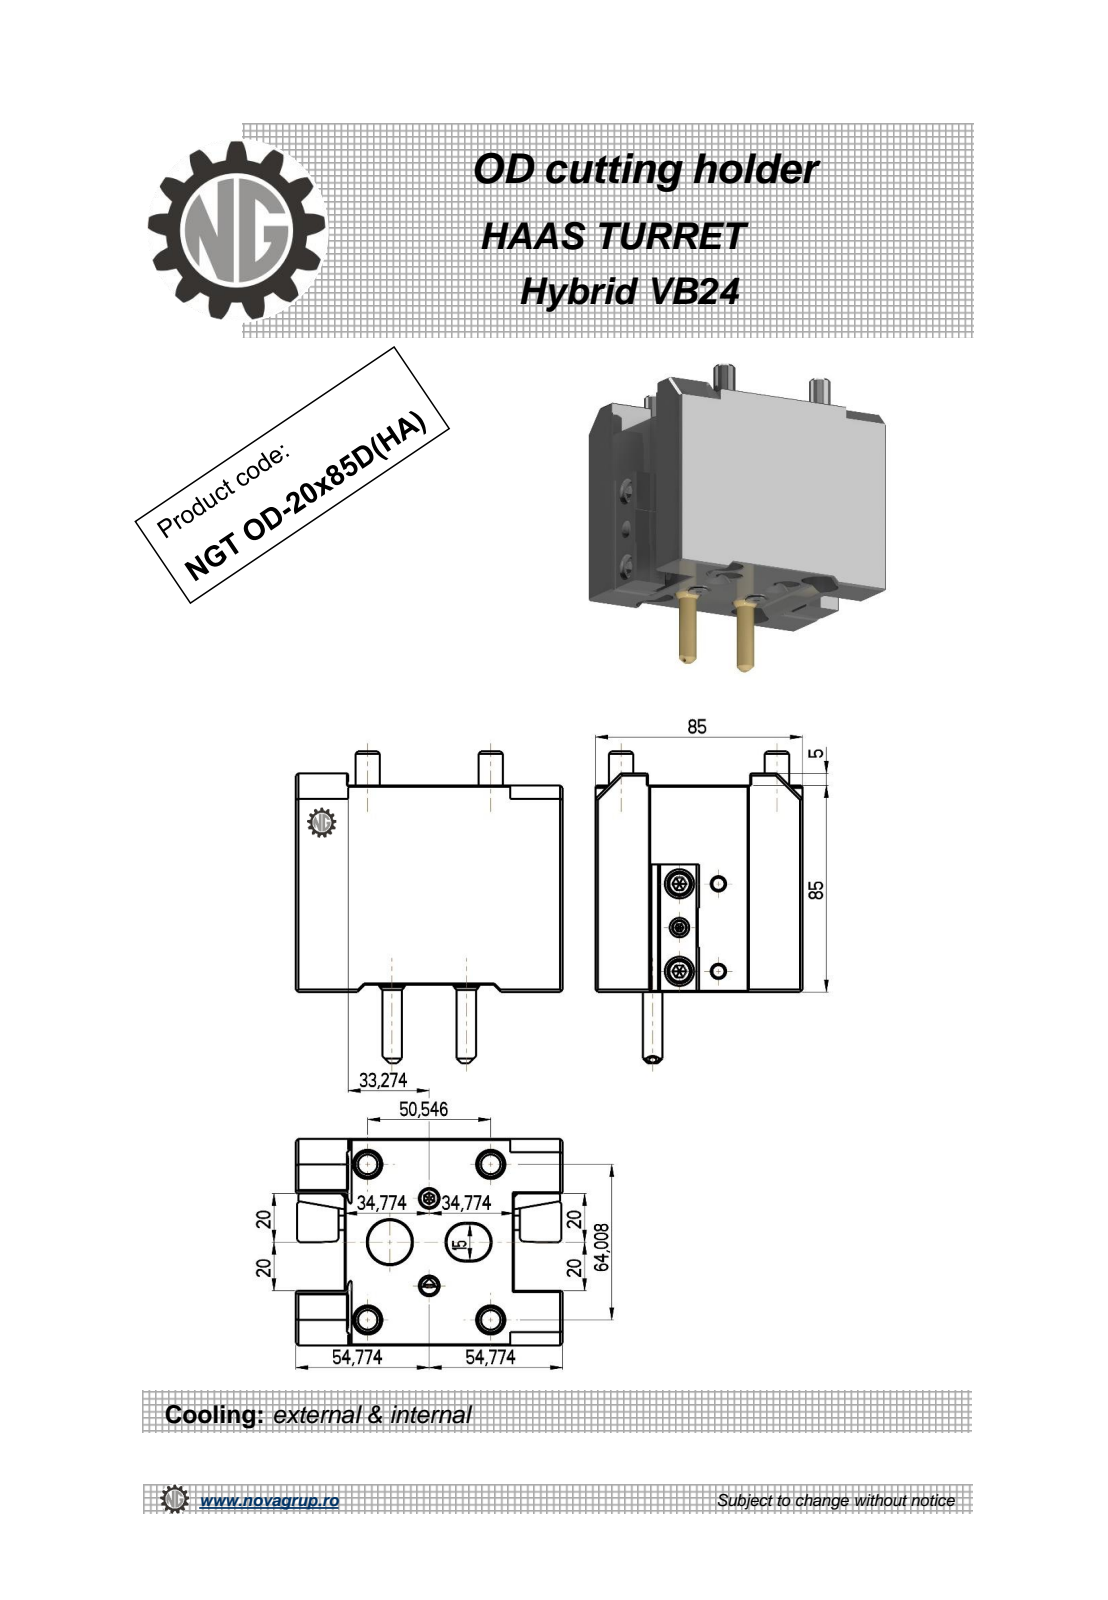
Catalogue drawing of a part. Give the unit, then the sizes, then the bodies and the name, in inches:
Units: inches
Overall size (bounding box): 5.053 × 4.313 × 3.346
Round holes (diameter × count): ⌀0.118 ×2, ⌀0.197 ×2, ⌀0.268 ×1, ⌀0.709 ×1
Round bosses / shafts (diameter × count): ⌀0.394 ×6, ⌀0.236 ×3, ⌀0.315 ×2
Partial cylindrical surfaces — rounded edges, fillets, slot ends (radius × count): R0.008 ×12, R0.016 ×6, R0.295 ×2, R0.039 ×1
Main face-to-face distances: 3.346, 0.787, 3.525, 0.886, 2.461, 3.228, 4.313, 2.738, 0.118, 0.02
Hole centre spacings: 1.576, 0.749, 0.953, 1.202, 1.446
Volume: 41.6 in³ · Surface area: 101.2 in²
Bodies: 1 solid, 279 faces (173 planar, 60 cylindrical, 46 other)
Part name (STEP PRODUCT): NGT_OD_20_85D_HA
STEP written by: PRO/ENGINEER BY PARAMETRIC TECHNOLOGY CORPORATION, 2010280 (CONFIG_CONTROL_DESIGN)
